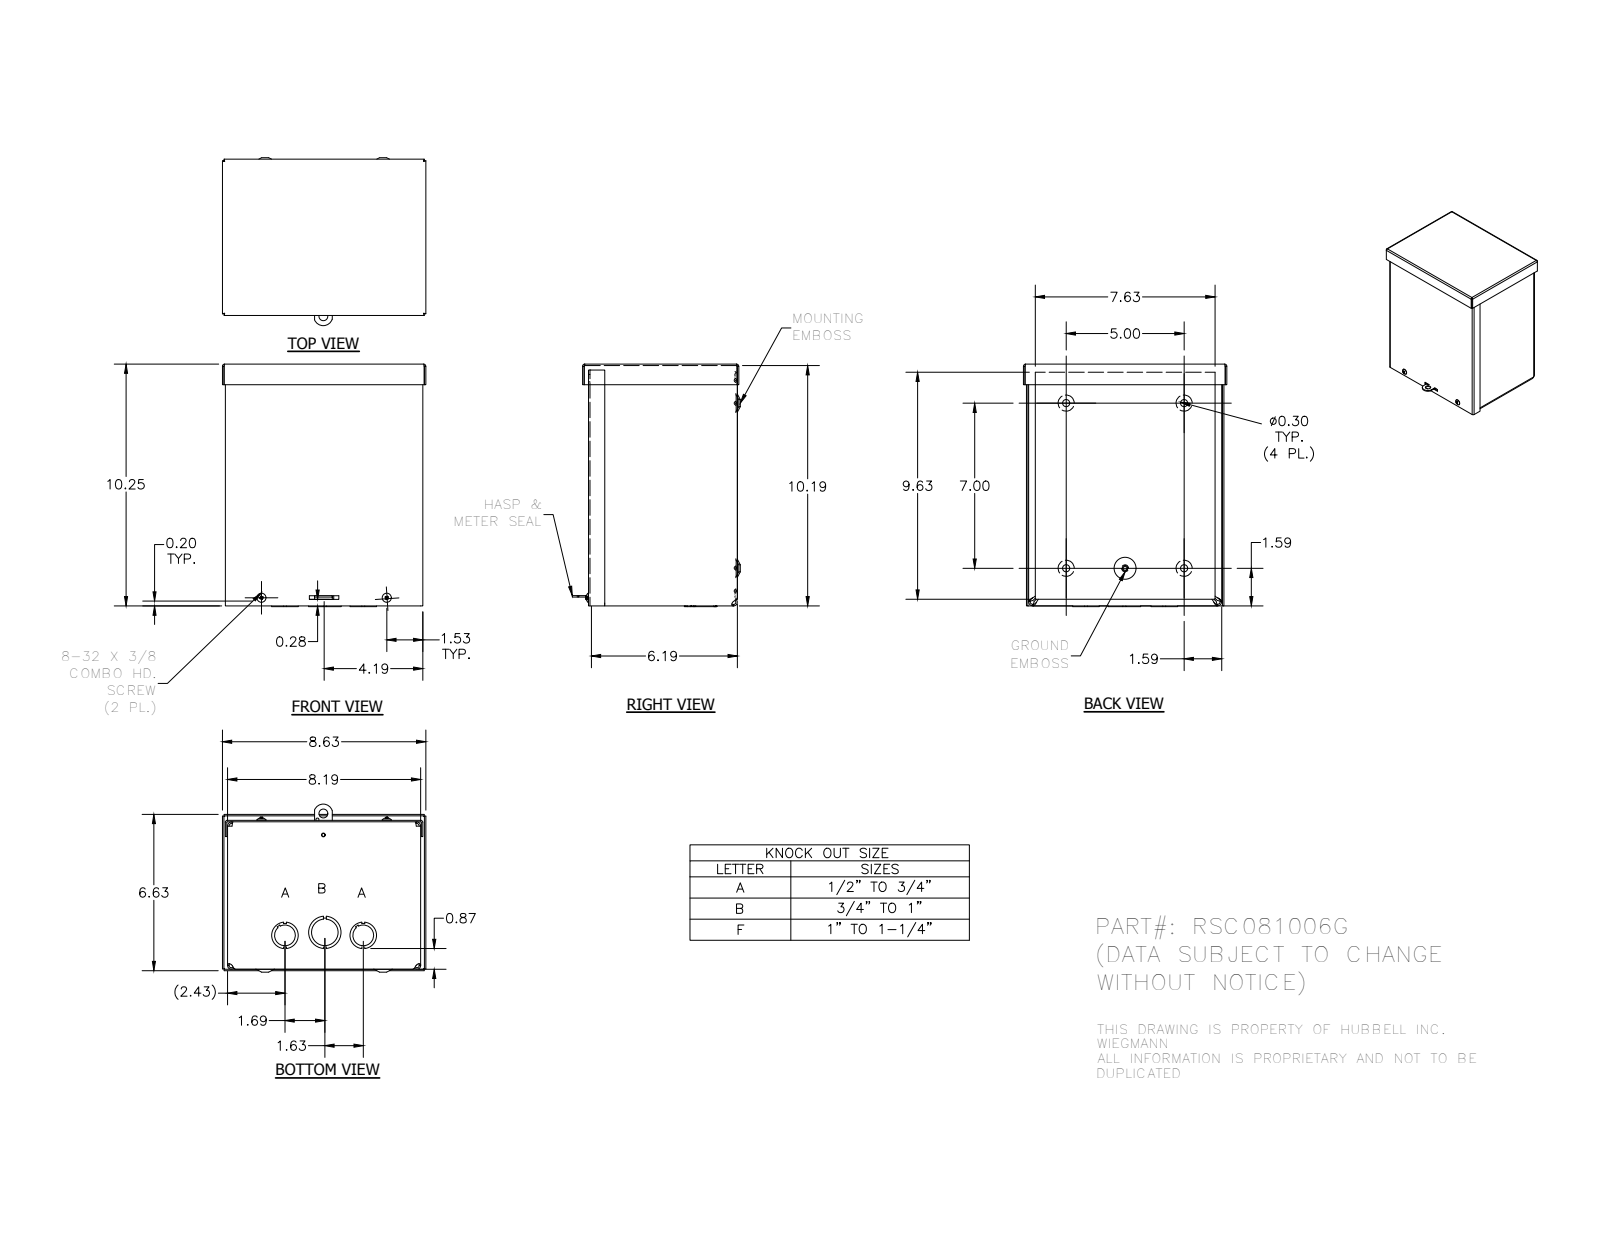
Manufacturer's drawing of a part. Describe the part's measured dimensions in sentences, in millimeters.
The part is named "RSC081006G_WRAP; RSC0810G_LID; RSC0806G_CAP; 3183 (+4 more)". Its 3-D file was written by "Autodesk Inventor 2014 (AUTOMOTIVE_DESIGN)". It is 7 solids with 503 faces: 238 planar, 121 cylindrical and 144 other. Overall it measures 261.12 by 219.07 by 180.97 millimeters. Its volume is 534 092 cubic millimeters and its surface area 687 862 square millimeters. Round holes: 4 of diameter 7.62, 4 of diameter 7.95, 3 of diameter 28.57, 2 of diameter 3.17, 2 of diameter 3.76, 2 of diameter 22.22, 1 of diameter 3.96, 1 of diameter 4.19, 1 of diameter 9.52, 1 of diameter 34.92. Round bosses or shafts: 2 of diameter 9.75, 2 of diameter 4.17, 1 of diameter 5.8. Partial cylindrical surfaces (rounded edges, fillets, slot ends): 10 of radius 0.25, 8 of radius 0.79, 8 of radius 2.37, 8 of radius 3.17, 8 of radius 4.75, 4 of radius 0.53, 4 of radius 0.79, 4 of radius 1.4. The main face-to-face distances are 1.58, 1.57, 206.39, 158.73, 257.19, 157.15, 1.59, 3.15, 160.32, 158.74. The hole center spacings are 27.24, 32.03, 63.5, 127, 134.95, 177.8, 188.79, 204.79.
